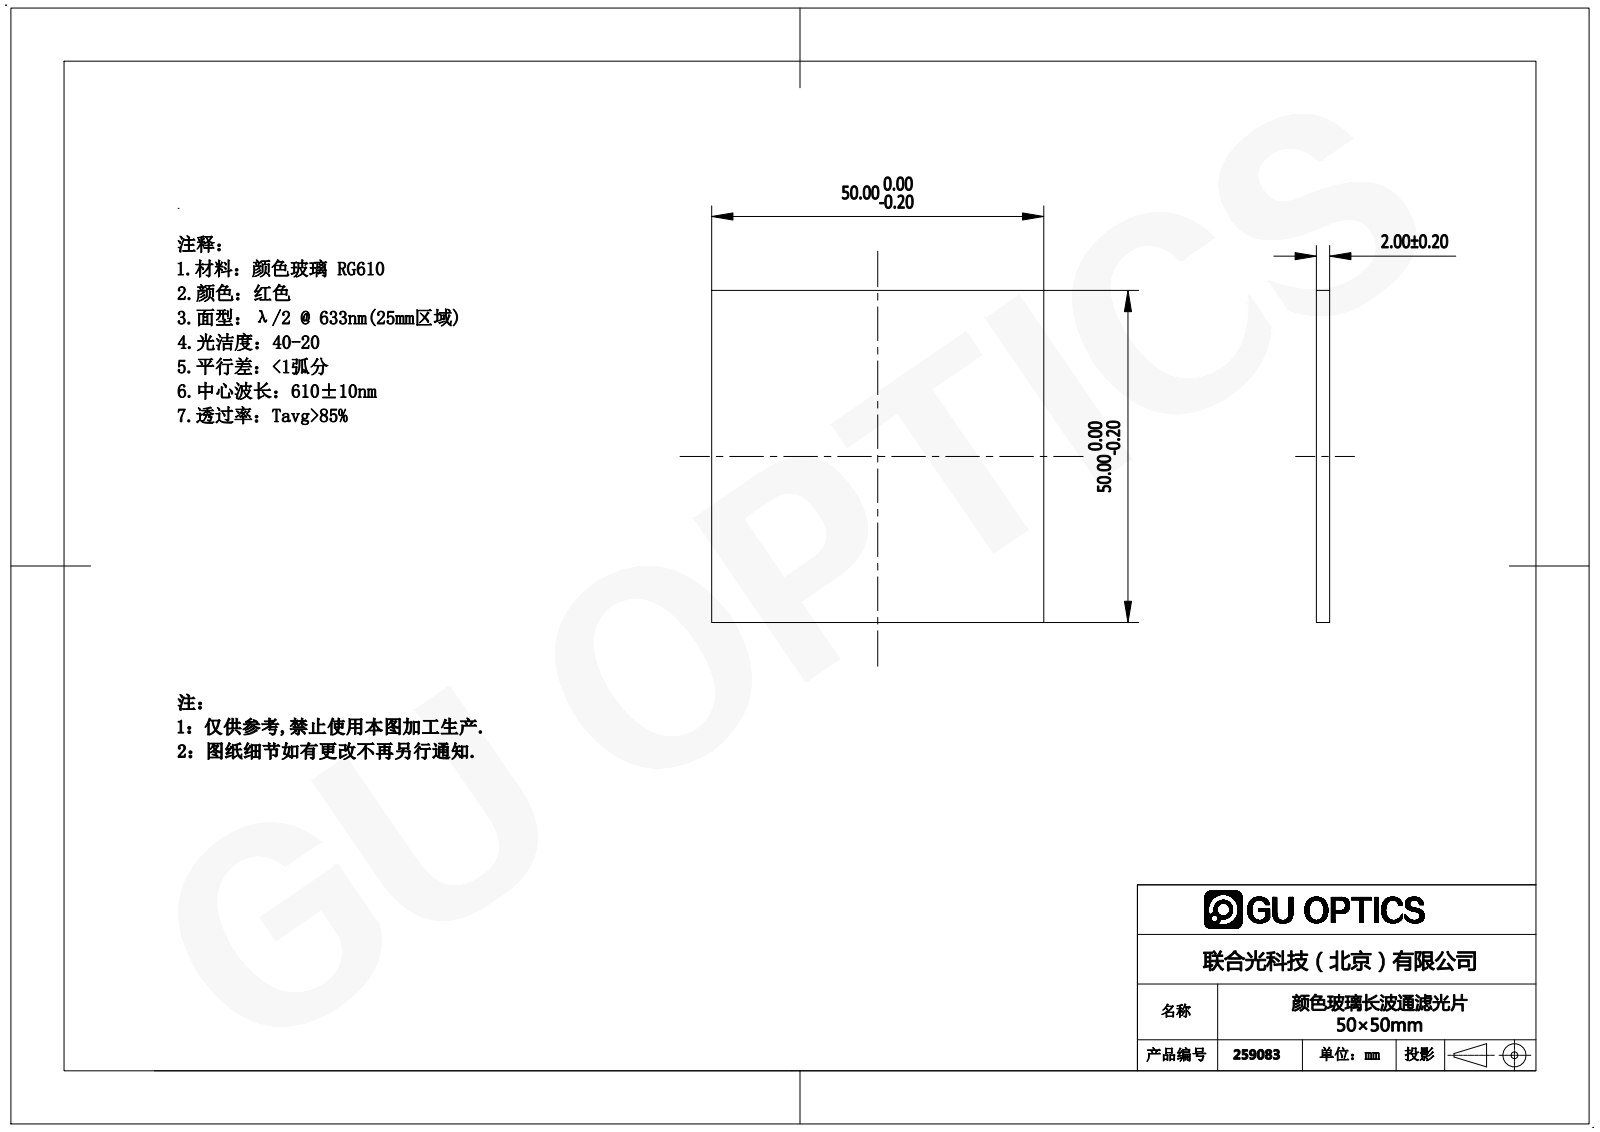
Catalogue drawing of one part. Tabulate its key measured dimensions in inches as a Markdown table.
| quantity | value |
| --- | --- |
| part name | 258515 |
| STEP written by | SolidWorks 2016 (CONFIG_CONTROL_DESIGN) |
| units | inches |
| bodies | 1 solid, 6 faces (6 planar, 0 cylindrical, 0 other) |
| overall size | 1.969 × 1.969 × 0.079 |
| volume | 0.305 in³ |
| surface area | 8.37 in² |
| main face-to-face distances | 0.079, 1.969 |
